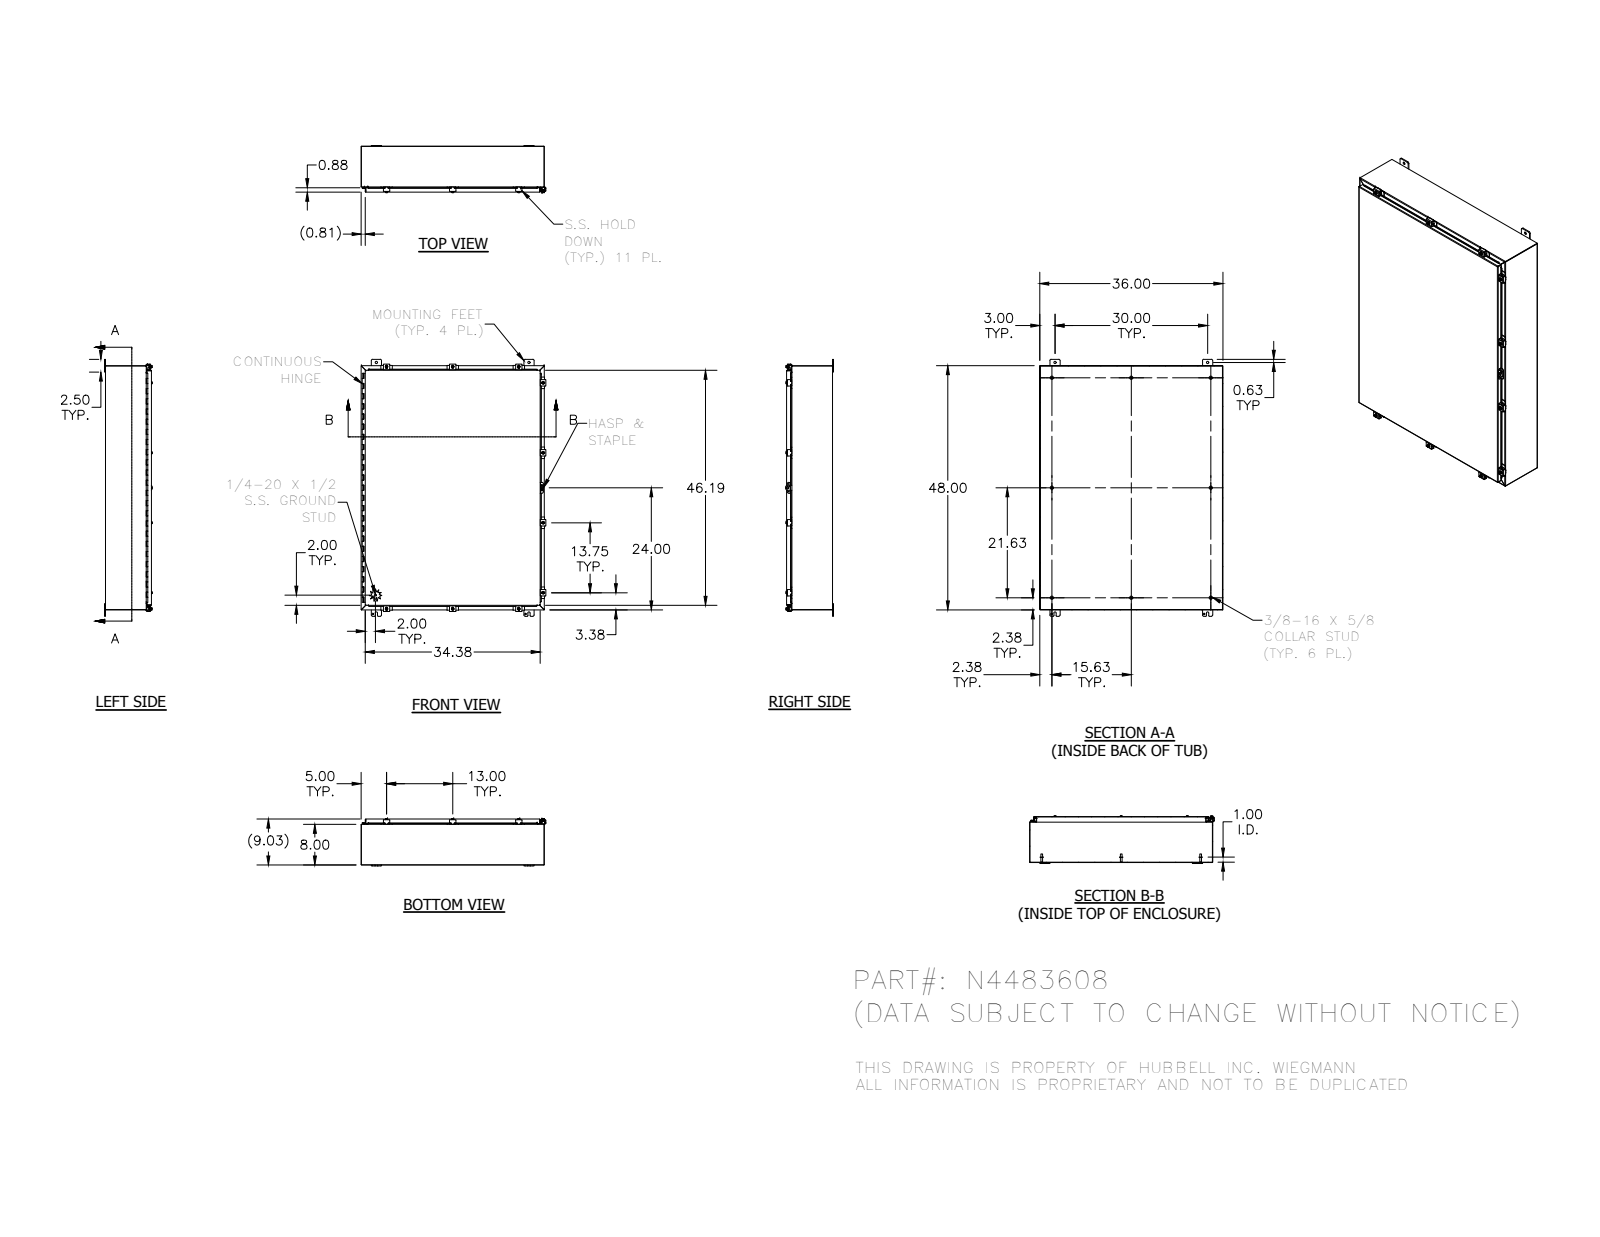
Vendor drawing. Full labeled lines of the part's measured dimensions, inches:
Part name (STEP PRODUCT): 328115L_1; 34840_1; HFW30825-2_1; 328115_1 (+8 more)
STEP written by: SolidWorks 2014 (AUTOMOTIVE_DESIGN)
Units: inches
Bodies: 73 solids, 2720 faces (1105 planar, 1190 cylindrical, 425 other)
Overall size (bounding box): 50.5 × 36.311 × 9.41
Volume: 414.5 in³ · Surface area: 10 953 in²
Round holes (diameter × count): ⌀0.211 ×10, ⌀0.281 ×10, ⌀0.3 ×10, ⌀0.313 ×4, ⌀0.438 ×4, ⌀0.11 ×3, ⌀0.125 ×1, ⌀0.156 ×1, ⌀0.5 ×1
Round bosses / shafts (diameter × count): ⌀0.25 ×12, ⌀0.52 ×10, ⌀0.5 ×10, ⌀0.35 ×10, ⌀0.625 ×8, ⌀0.33 ×8, ⌀0.337 ×1, ⌀0.12 ×1
Partial cylindrical surfaces — rounded edges, fillets, slot ends (radius × count): R0.03 ×117, R0.125 ×41, R0.25 ×37, R0.062 ×22, R0.031 ×21, R0.105 ×21, R0.141 ×20, R0.1 ×14
Main face-to-face distances: 0.074, 8.959, 8.885, 9.033, 35.926, 47.926, 7.926, 1.033, 35.852, 36
Hole centre spacings: 1.593, 13, 30, 48, 49.36, 56.604, 13.75, 47.617
